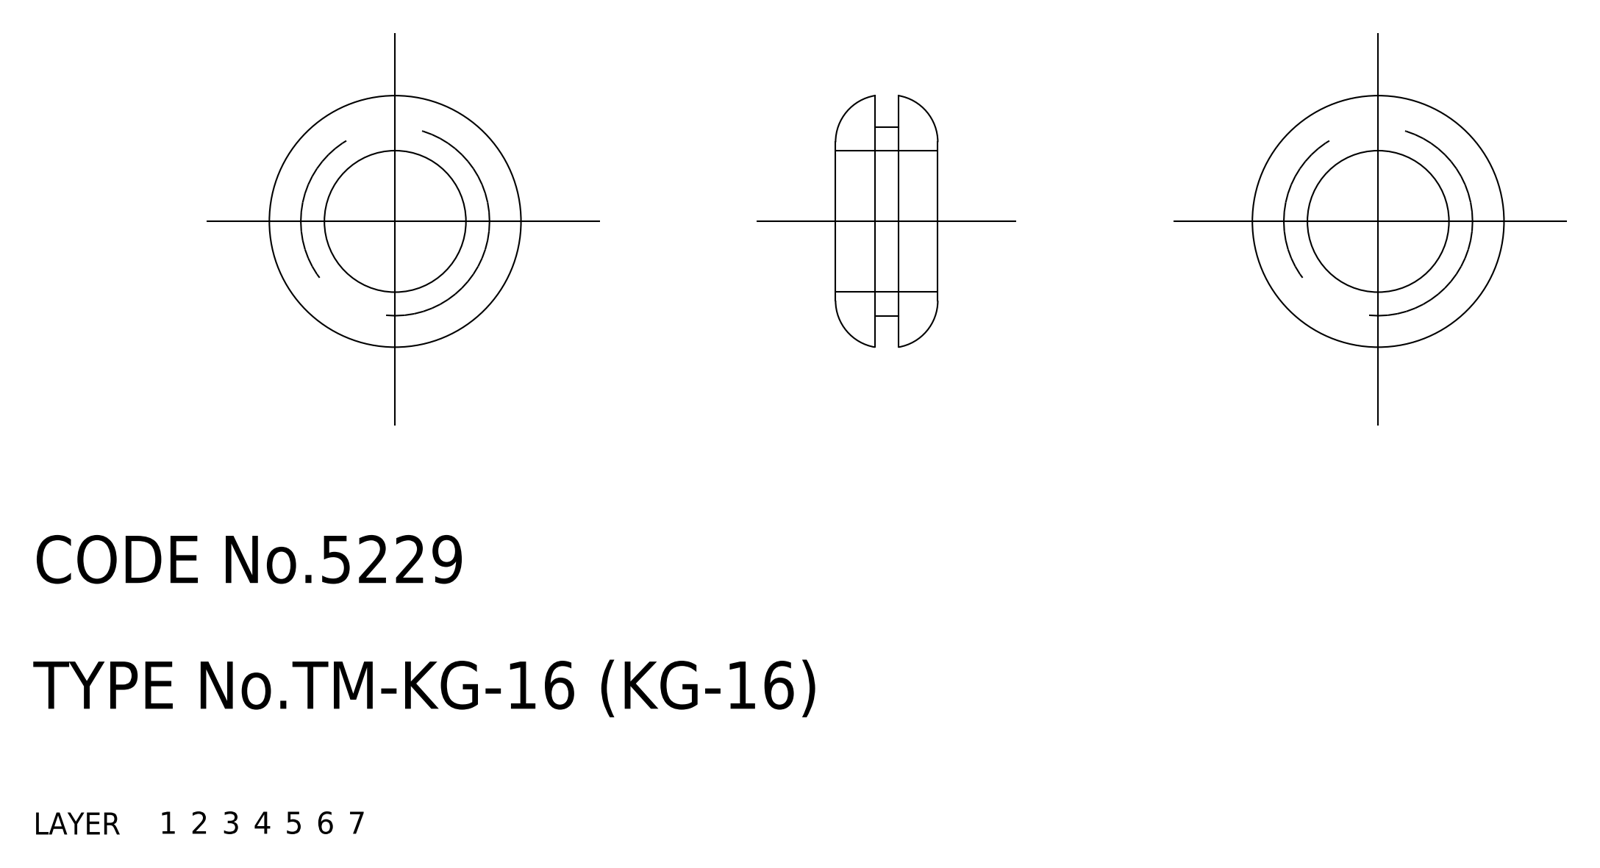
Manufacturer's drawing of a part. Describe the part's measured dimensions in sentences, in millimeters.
The part is named "grommet". Its 3-D file was written by "CADfix (AUTOMOTIVE_DESIGN)". It is 1 solid with 12 faces: 0 planar, 0 cylindrical and 12 other. Overall it measures 16 by 16 by 6.5 millimeters. Its volume is 595 cubic millimeters and its surface area 810 square millimeters.
